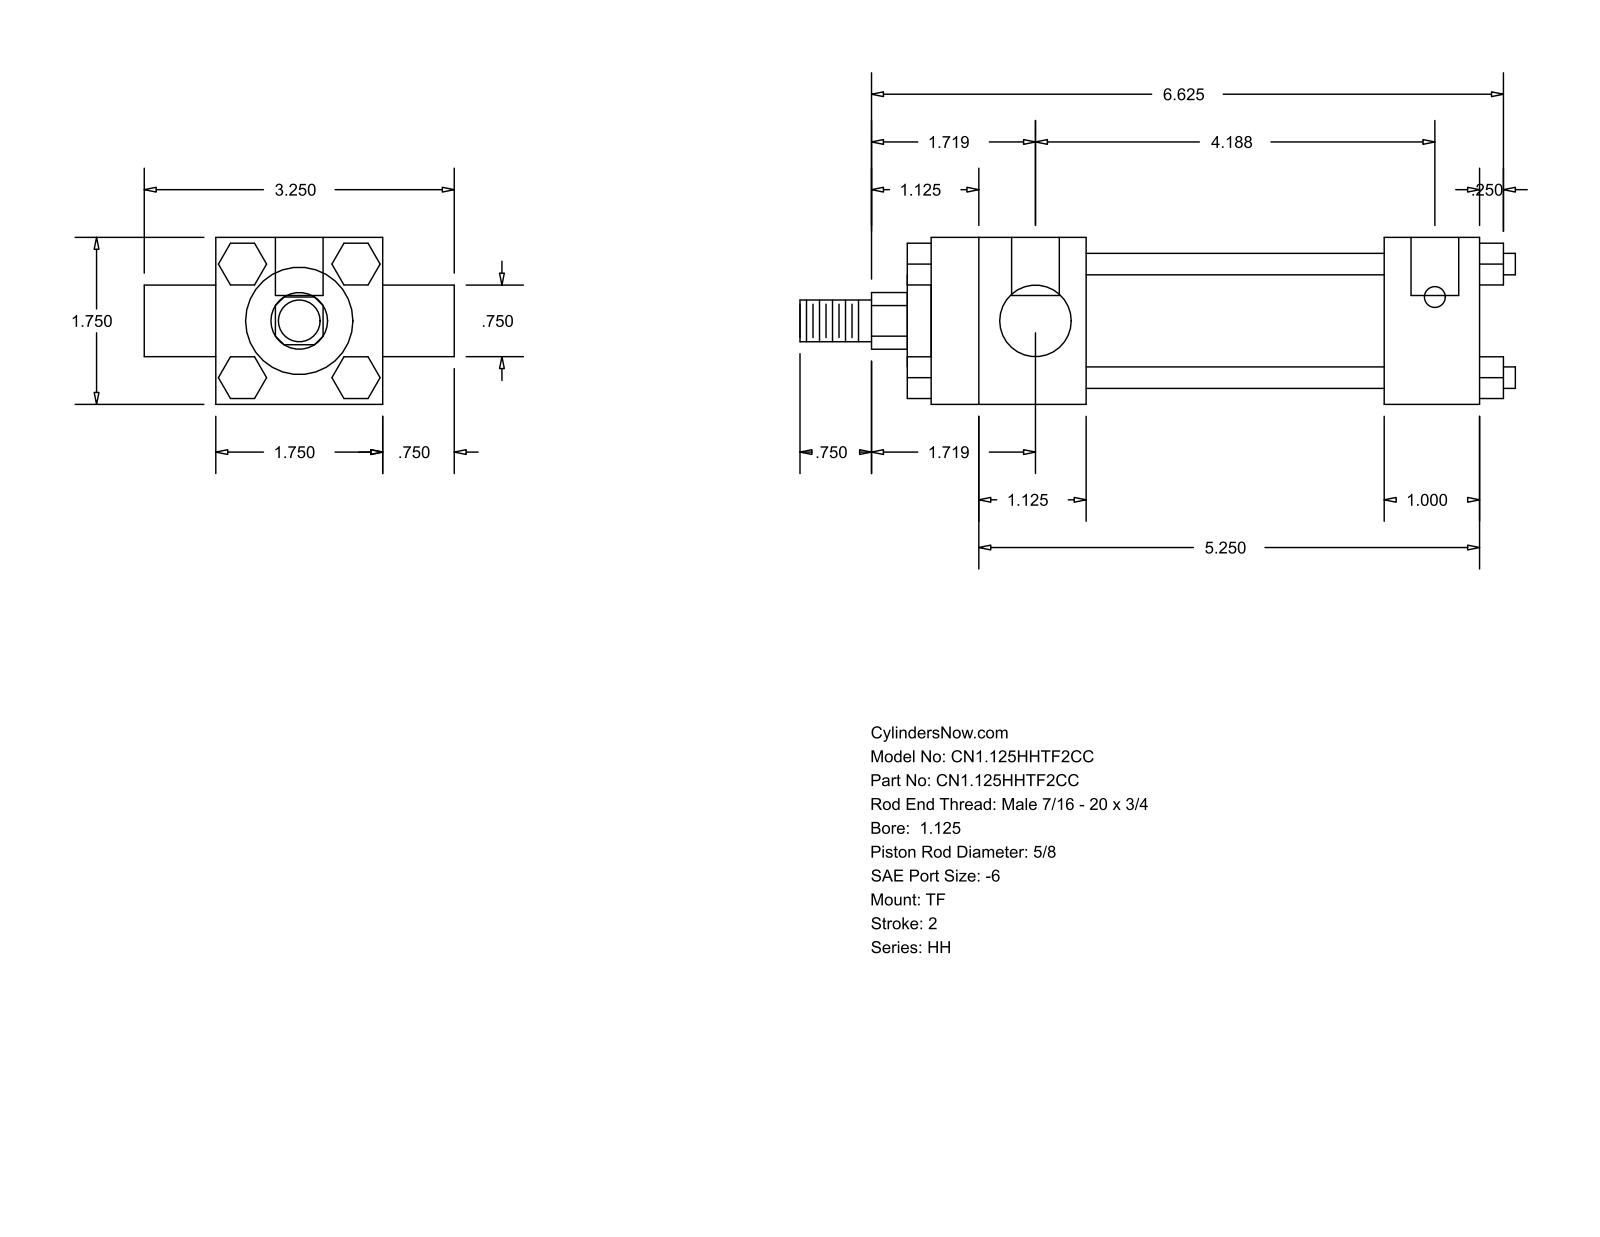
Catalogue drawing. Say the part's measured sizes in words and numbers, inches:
The part is named "HH_TF__0112_0.625". Its 3-D file was written by "GSSL Pune (CONFIG_CONTROL_DESIGN)". It is 0 solids with 120 faces: 92 planar, 28 cylindrical and 0 other. Overall it measures 7.5 by 3.25 by 1.75 inches. Round holes: 3 of diameter 0.219, 2 of diameter 0.5. Round bosses or shafts: 4 of diameter 0.225, 1 of diameter 1.375, 1 of diameter 1.125, 1 of diameter 0.75, 1 of diameter 0.625, 1 of diameter 0.437. Partial cylindrical surfaces (rounded edges, fillets, slot ends): 1 of radius 0.297. The main face-to-face distances are 1.75, 0.25, 6, 0.437, 1, 3.125, 4.125, 1.625, 4.75, 5.75. The hole center spacings are 0.125, 4.063, 4.187.
